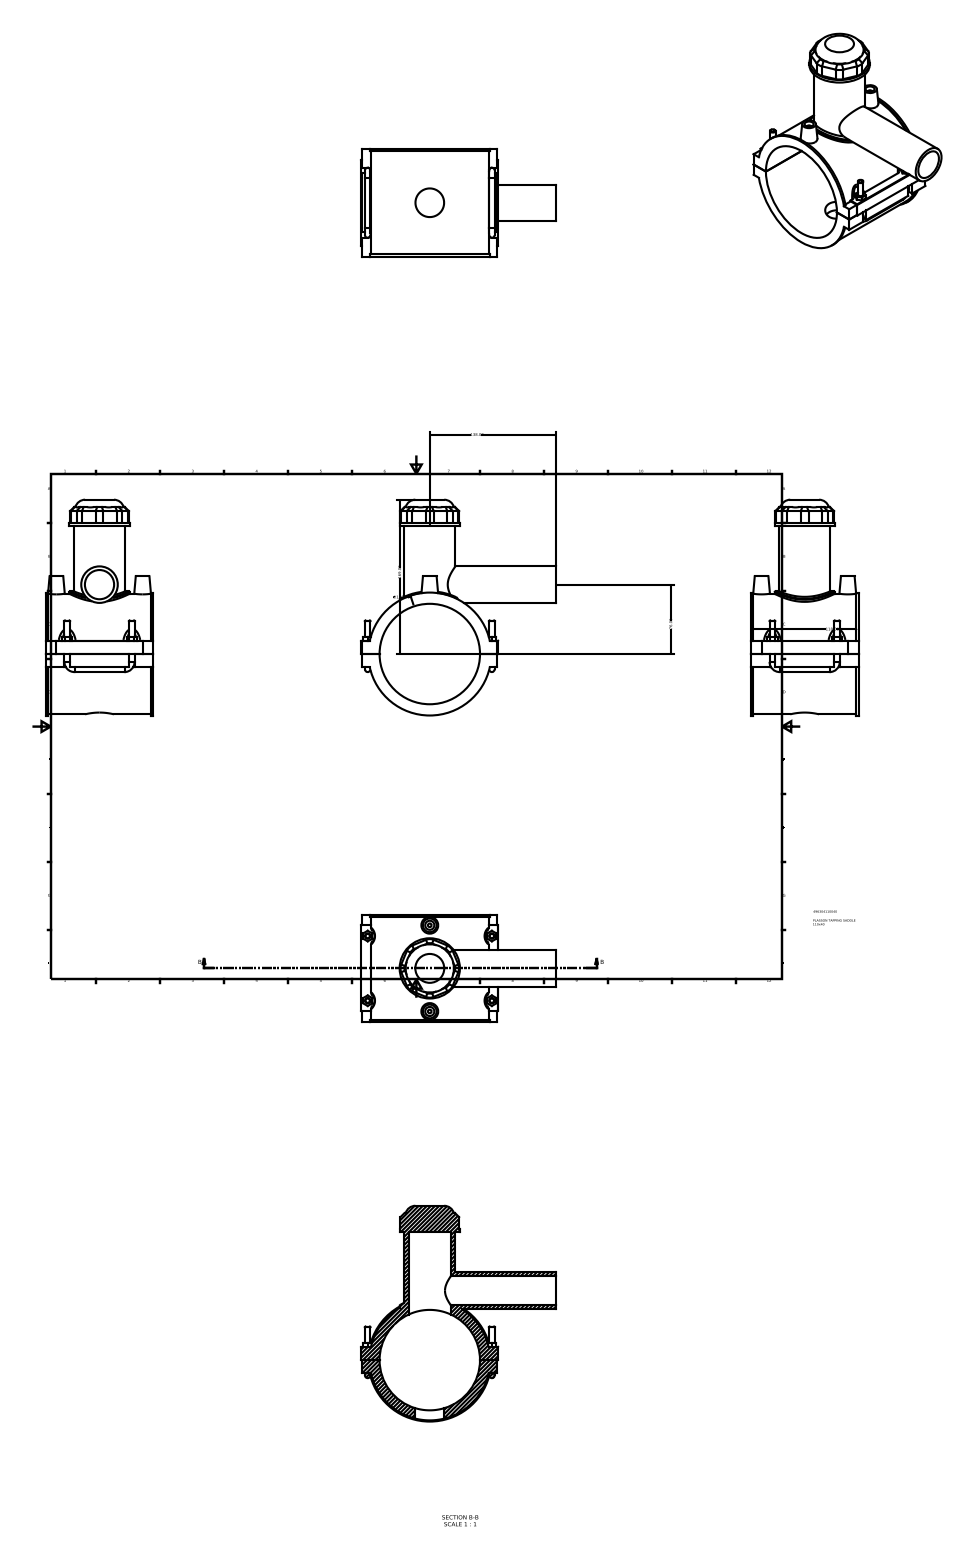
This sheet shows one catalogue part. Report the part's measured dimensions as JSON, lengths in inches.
{"part_name": "496304110040", "step_written_by": "Autodesk Inventor 2015 (AUTOMOTIVE_DESIGN)", "units": "inches", "bodies": {"solids": 1, "faces": 188, "planar": 117, "cylindrical": 47, "other": 24}, "overall_size": [9.304, 8.386, 4.646], "volume_in3": 44.29, "surface_area_in2": 278.3, "round_holes": [[0.394, 2], [1.235, 1], [1.26, 1], [1.819, 1], [4.331, 1]], "round_bosses_or_shafts": [[0.236, 6], [0.157, 2], [5.301, 1], [5.197, 1], [2.598, 1], [2.209, 1], [1.575, 1]], "partial_cylinders_radius": [[0.433, 8], [0.118, 4], [0.295, 4], [0.02, 1], [2.702, 1]], "face_to_face_distances": [4.646, 0.039, 6.073, 5.866, 5.533, 5.53, 1.122, 0.539, 0.543, 0.583], "hole_center_spacings": [1.858, 3.717]}
